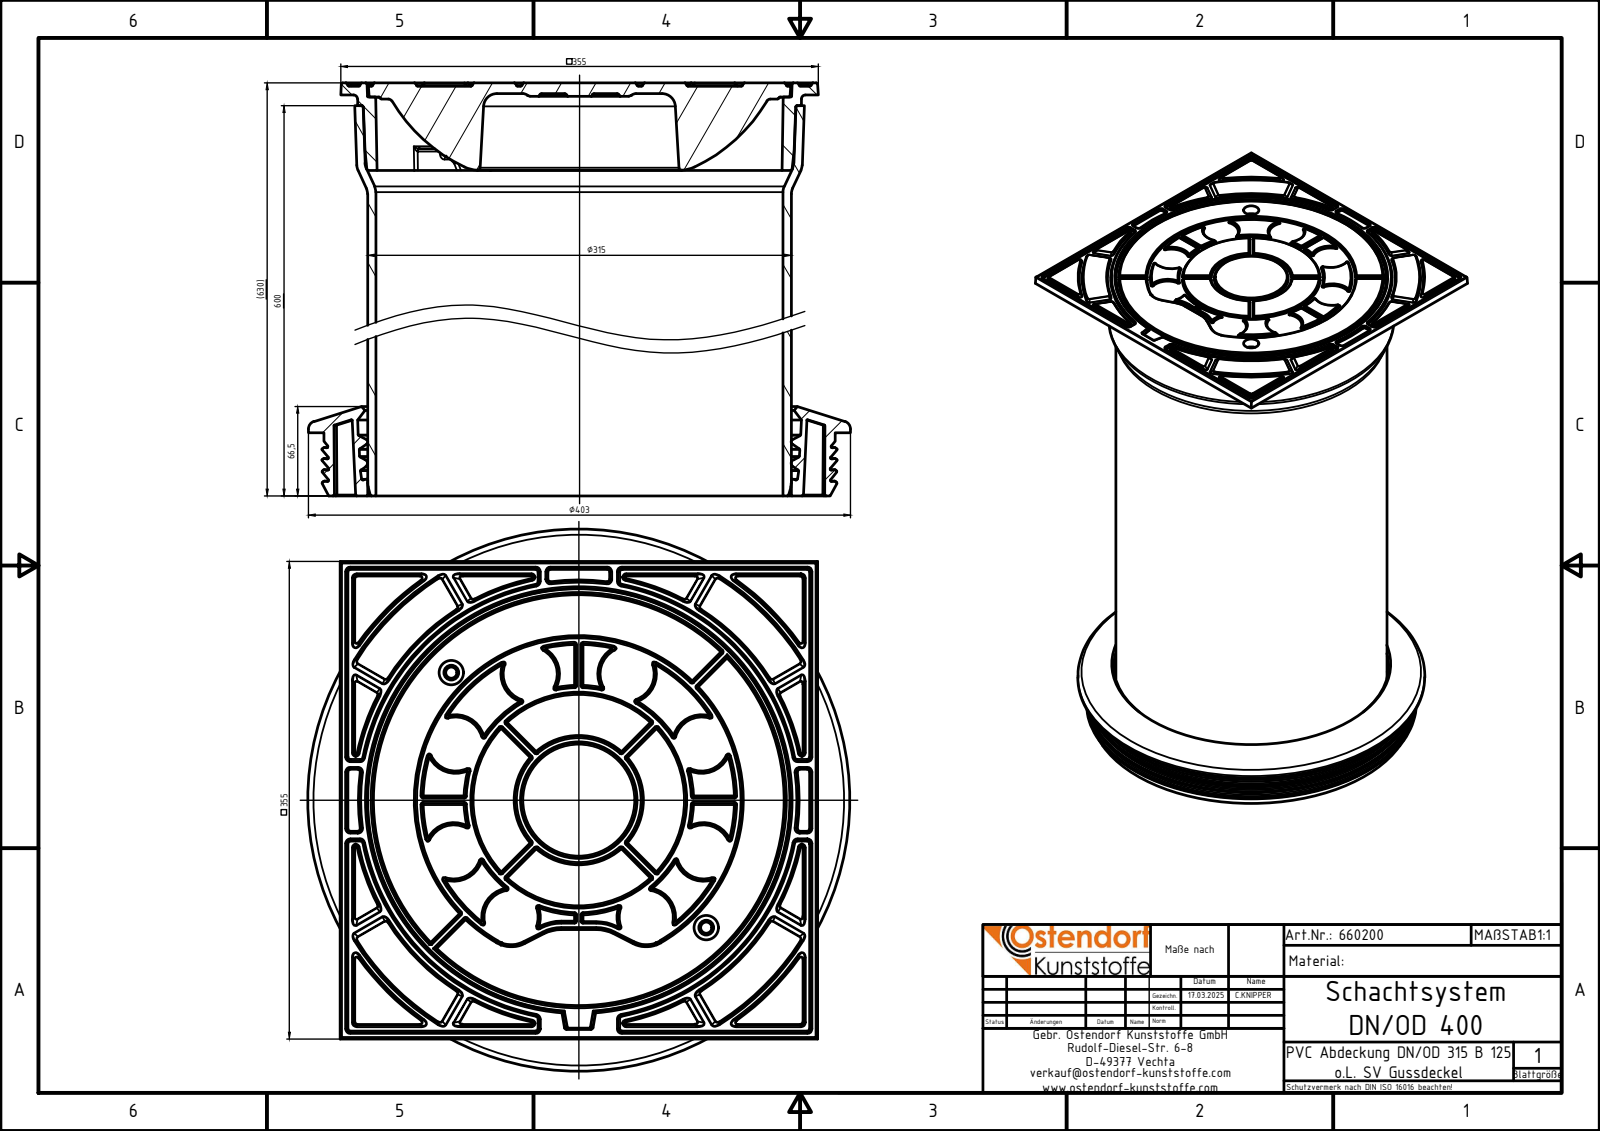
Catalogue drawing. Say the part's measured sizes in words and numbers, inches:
The part is named "660200z; 660205_Dichtungz; 990010_1z; 990010_2z (+1 more)". Its 3-D file was written by "Autodesk Inventor 2024 (AUTOMOTIVE_DESIGN)". It is 4 solids with 1501 faces: 200 planar, 241 cylindrical and 1060 other. Overall it measures 24.291 by 15.866 by 15.866 inches. Its volume is 496.1 cubic inches and its surface area 3 165 square inches. Round holes: 2 of diameter 0.33, 2 of diameter 0.433, 2 of diameter 0.709, 1 of diameter 11.913, 1 of diameter 12.402. Round bosses or shafts: 1 of diameter 15.866, 1 of diameter 14.961, 1 of diameter 12.992. Partial cylindrical surfaces (rounded edges, fillets, slot ends): 153 of radius 0.039, 8 of radius 0.079, 8 of radius 0.098. The main face-to-face distances are 0.354, 0.098, 0.256, 0.315, 23.937, 24.193, 24.291, 0.059, 1.85, 22.087. The hole center spacings are 5.276, 10.551.
